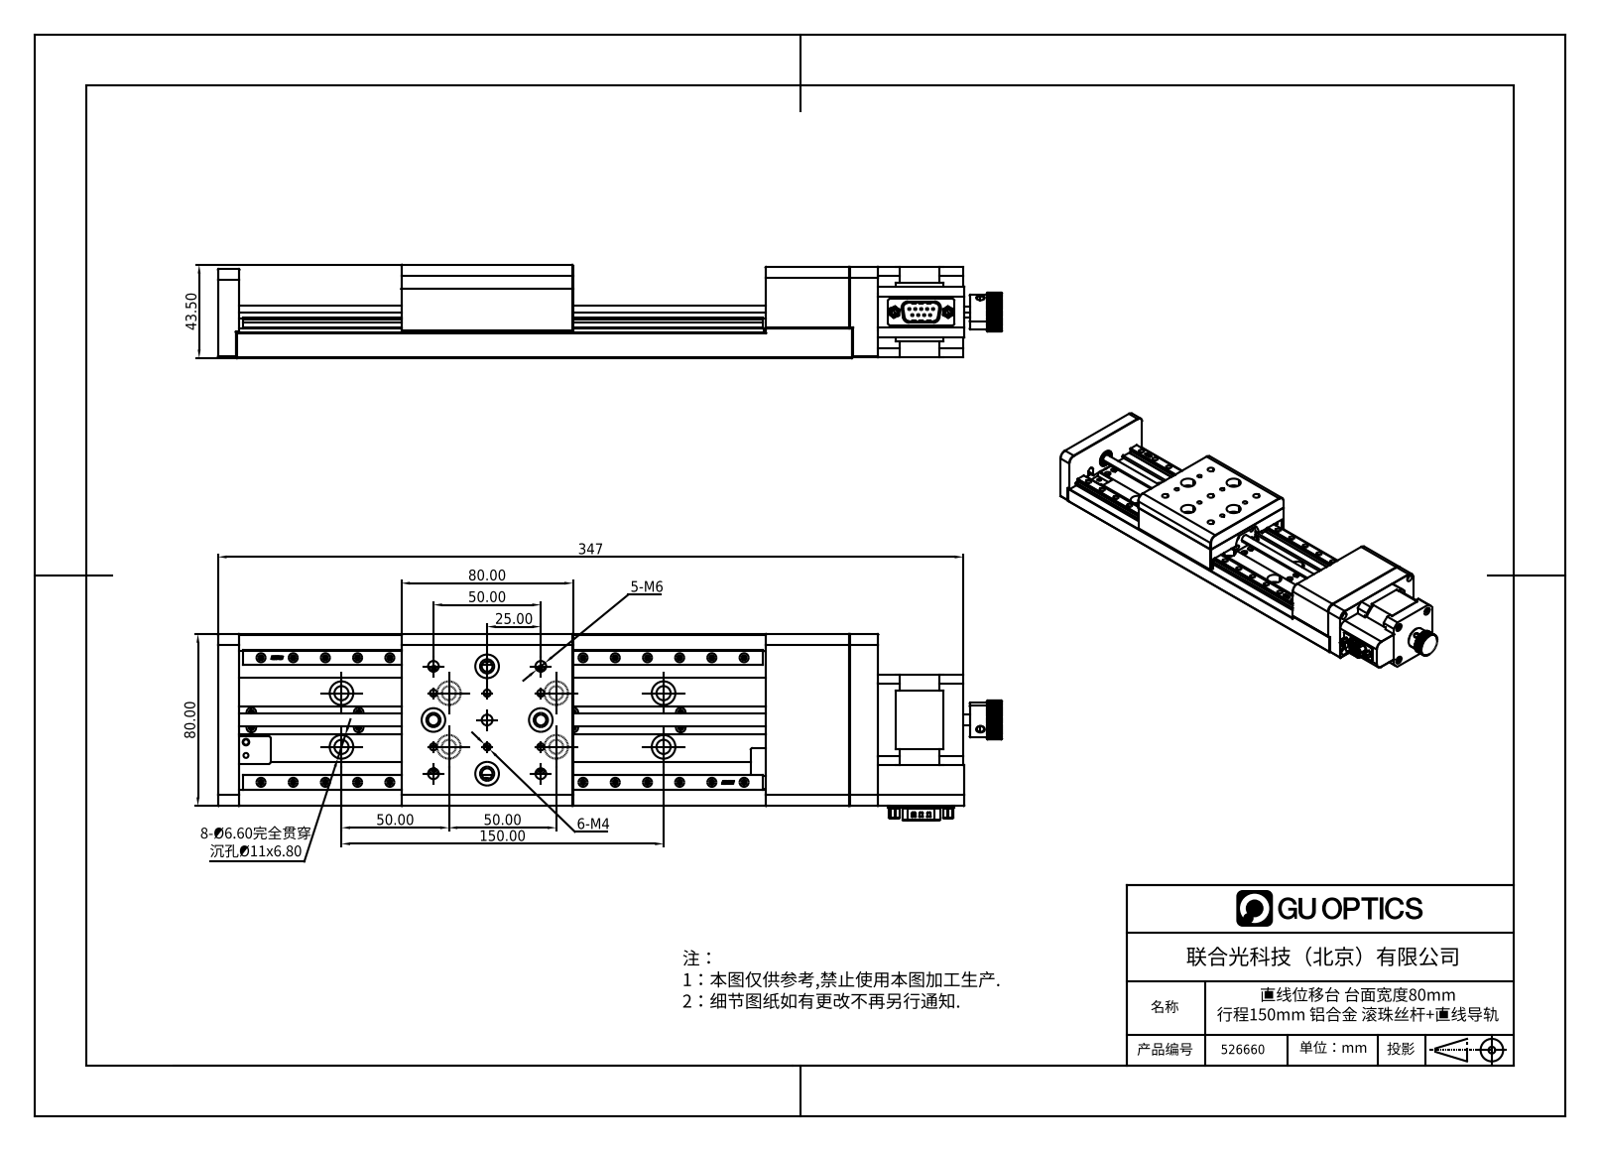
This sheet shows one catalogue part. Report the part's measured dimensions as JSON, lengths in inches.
{"part_name": "FMS80-150", "step_written_by": "SolidWorks 2017 (AUTOMOTIVE_DESIGN)", "units": "inches", "bodies": {"solids": 29, "faces": 2994, "planar": 962, "cylindrical": 1130, "other": 902}, "overall_size": [14.374, 3.417, 1.713], "volume_in3": 37.62, "surface_area_in2": 320.4, "round_holes": [[0.094, 60], [0.063, 46], [0.165, 32], [0.197, 25], [0.098, 16], [0.169, 16], [0.062, 12], [0.134, 12], [0.26, 12], [0.433, 12], [0.043, 9], [0.13, 9]], "round_bosses_or_shafts": [[0.059, 13], [0.039, 9], [0.197, 5], [0.024, 4], [0.118, 2], [0.866, 1], [0.63, 1], [0.472, 1]], "partial_cylinders_radius": [[0.02, 36], [0.039, 33], [0.197, 26], [0.016, 10], [0.012, 6], [0.079, 5], [0.028, 4], [0.051, 4]], "face_to_face_distances": [0.02, 1.26, 0.453, 0.079, 0.472, 0.807, 1.28, 0.531, 0.394, 0.551], "hole_center_spacings": [1.969, 3.937, 1.988, 0.124, 0.474, 0.704, 1.691, 1.769]}
